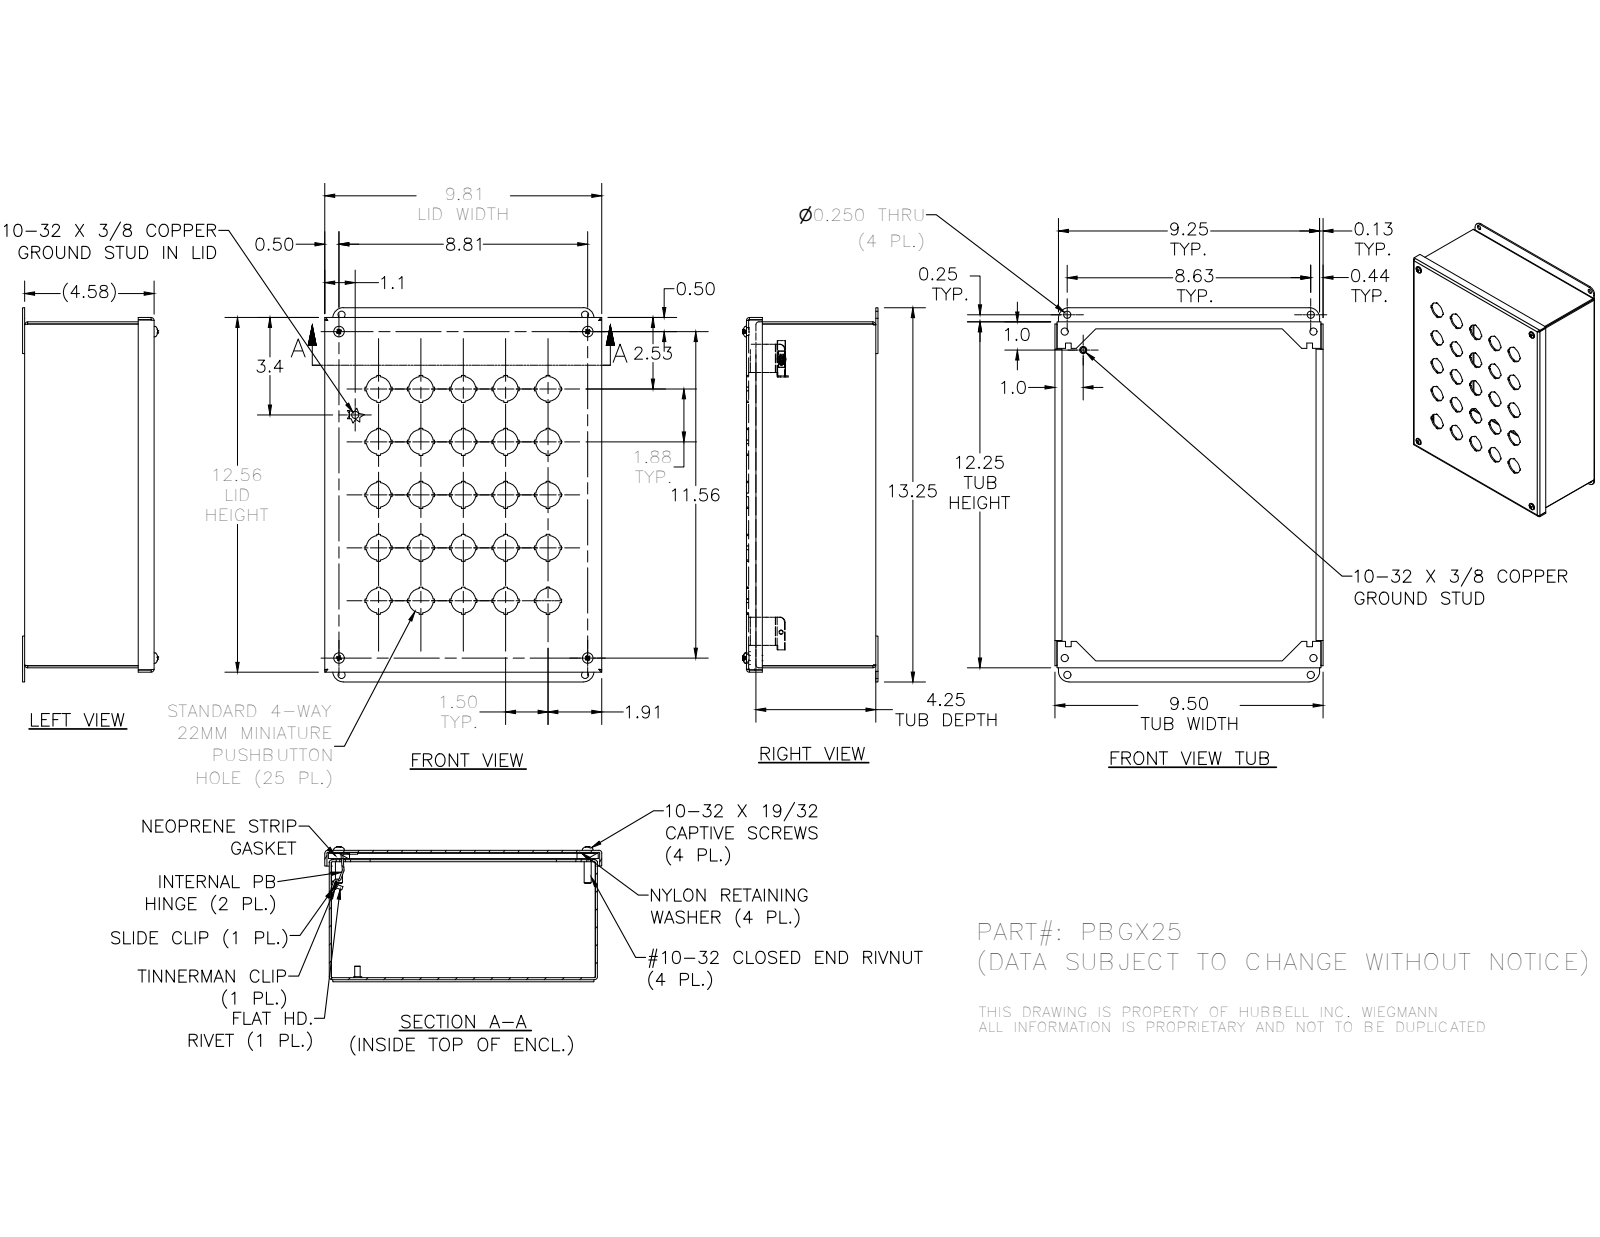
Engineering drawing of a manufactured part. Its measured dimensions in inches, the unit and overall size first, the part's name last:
Units: inches
Overall size (bounding box): 13.25 × 9.81 × 4.786
Round holes (diameter × count): ⌀0.875 ×25, ⌀0.156 ×4, ⌀0.196 ×4, ⌀0.25 ×4, ⌀0.257 ×4, ⌀0.278 ×4, ⌀0.281 ×4, ⌀0.313 ×4, ⌀0.14 ×2
Round bosses / shafts (diameter × count): ⌀0.19 ×6, ⌀0.453 ×4, ⌀0.406 ×4, ⌀0.373 ×4, ⌀0.248 ×4, ⌀0.25 ×3, ⌀0.125 ×1
Partial cylindrical surfaces — rounded edges, fillets, slot ends (radius × count): R0.031 ×12, R0.105 ×12, R0.188 ×6, R0.089 ×4, R0.09 ×4, R0.375 ×4, R0.031 ×3, R0.063 ×3
Main face-to-face distances: 0.074, 4.508, 4.582, 4.434, 9.426, 12.176, 9.5, 9.352, 0.155, 12.25
Hole centre spacings: 2.401, 3.538, 1.5, 4.039, 3, 3.75, 1.875, 4.802
Volume: 40.23 in³ · Surface area: 1 036 in²
Bodies: 25 solids, 1009 faces (663 planar, 232 cylindrical, 114 other)
Part name (STEP PRODUCT): 316265-PBGX25; PBGX25BKP; 34984; 3285 (+8 more)
STEP written by: Autodesk Inventor 2016 (AUTOMOTIVE_DESIGN)
